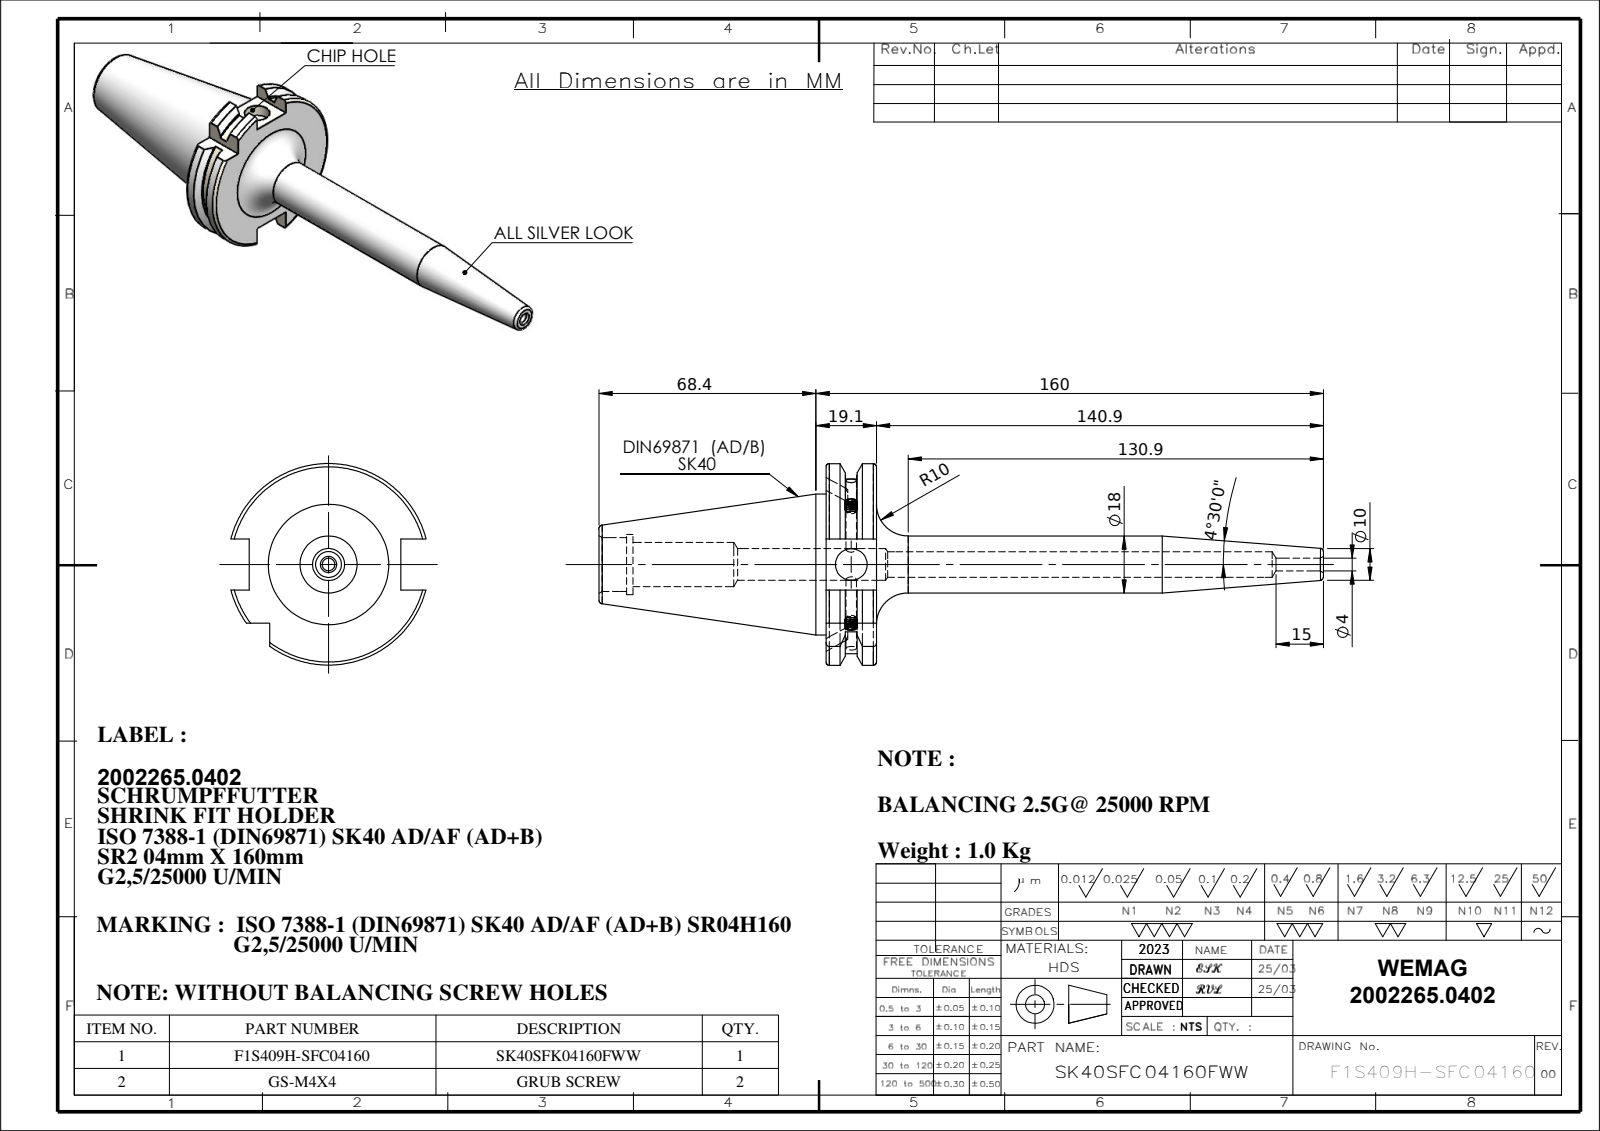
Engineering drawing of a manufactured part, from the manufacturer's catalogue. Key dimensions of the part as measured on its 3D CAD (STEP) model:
Part name (STEP PRODUCT): GS-M4X4_DIN 913 - M4 x 4-N; SK40SFC04160FWW; 91406-SR204160
STEP written by: SolidWorks 2018 (CONFIG_CONTROL_DESIGN)
Units: millimetres
Bodies: 3 solids, 196 faces (46 planar, 54 cylindrical, 96 other)
Overall size (bounding box): 228.4 × 63.55 × 61.48
Volume: 127 570 mm³ · Surface area: 31 472 mm²
Round holes (diameter × count): ⌀10 ×2, ⌀3.3 ×1, ⌀3.99 ×1, ⌀8 ×1, ⌀14 ×1, ⌀17 ×1, ⌀19 ×1
Round bosses / shafts (diameter × count): ⌀4 ×2, ⌀44.45 ×1, ⌀18 ×1
Partial cylindrical surfaces — rounded edges, fillets, slot ends (radius × count): R28.12 ×1, R31.77 ×1
Main face-to-face distances: 15.9, 16.1, 47.8, 71.6, 87.5, 10.7, 60.9, 76.8, 77.62, 66.92
